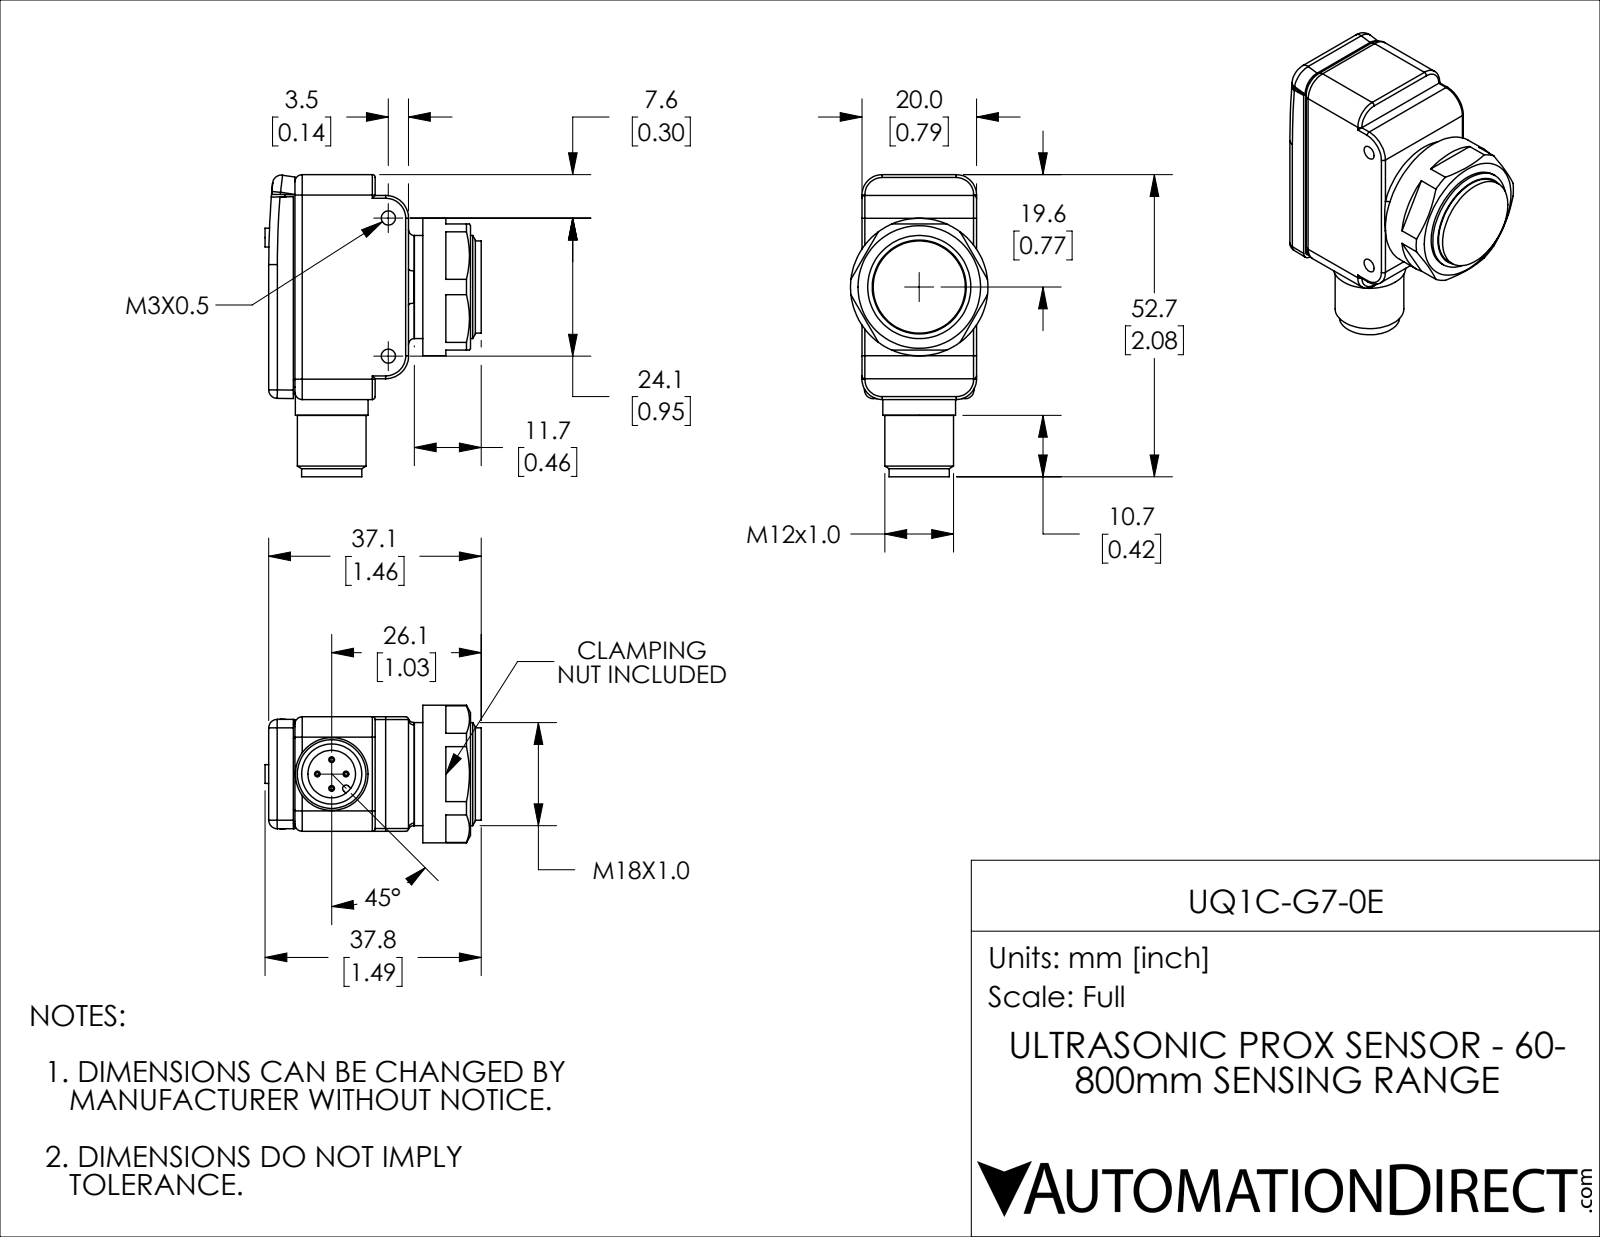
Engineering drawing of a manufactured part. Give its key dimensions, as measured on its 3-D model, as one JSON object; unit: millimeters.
{"part_name": "UQ1C-G7-0E", "step_written_by": "SolidWorks 2018 (AUTOMOTIVE_DESIGN)", "units": "millimeters", "bodies": {"solids": 7, "faces": 203, "planar": 81, "cylindrical": 72, "other": 50}, "overall_size": [52.73, 37.75, 24], "volume_mm3": 22757, "surface_area_mm2": 11051, "round_holes": [[2.46, 2], [3.3, 1], [8.3, 1]], "round_bosses_or_shafts": [[1, 4], [24, 1], [18, 1], [16.1, 1], [12.7, 1], [12, 1], [10.5, 1]], "partial_cylinders_radius": [[0.5, 10], [1.5, 6], [1.25, 4], [3.55, 4], [3, 2], [4, 2], [150, 2], [0.6, 1]], "face_to_face_distances": [2.3, 20, 23.13, 20.83, 2.29, 4.59, 25.42, 11.67, 37.09, 34.8], "hole_center_spacings": [24.1]}
